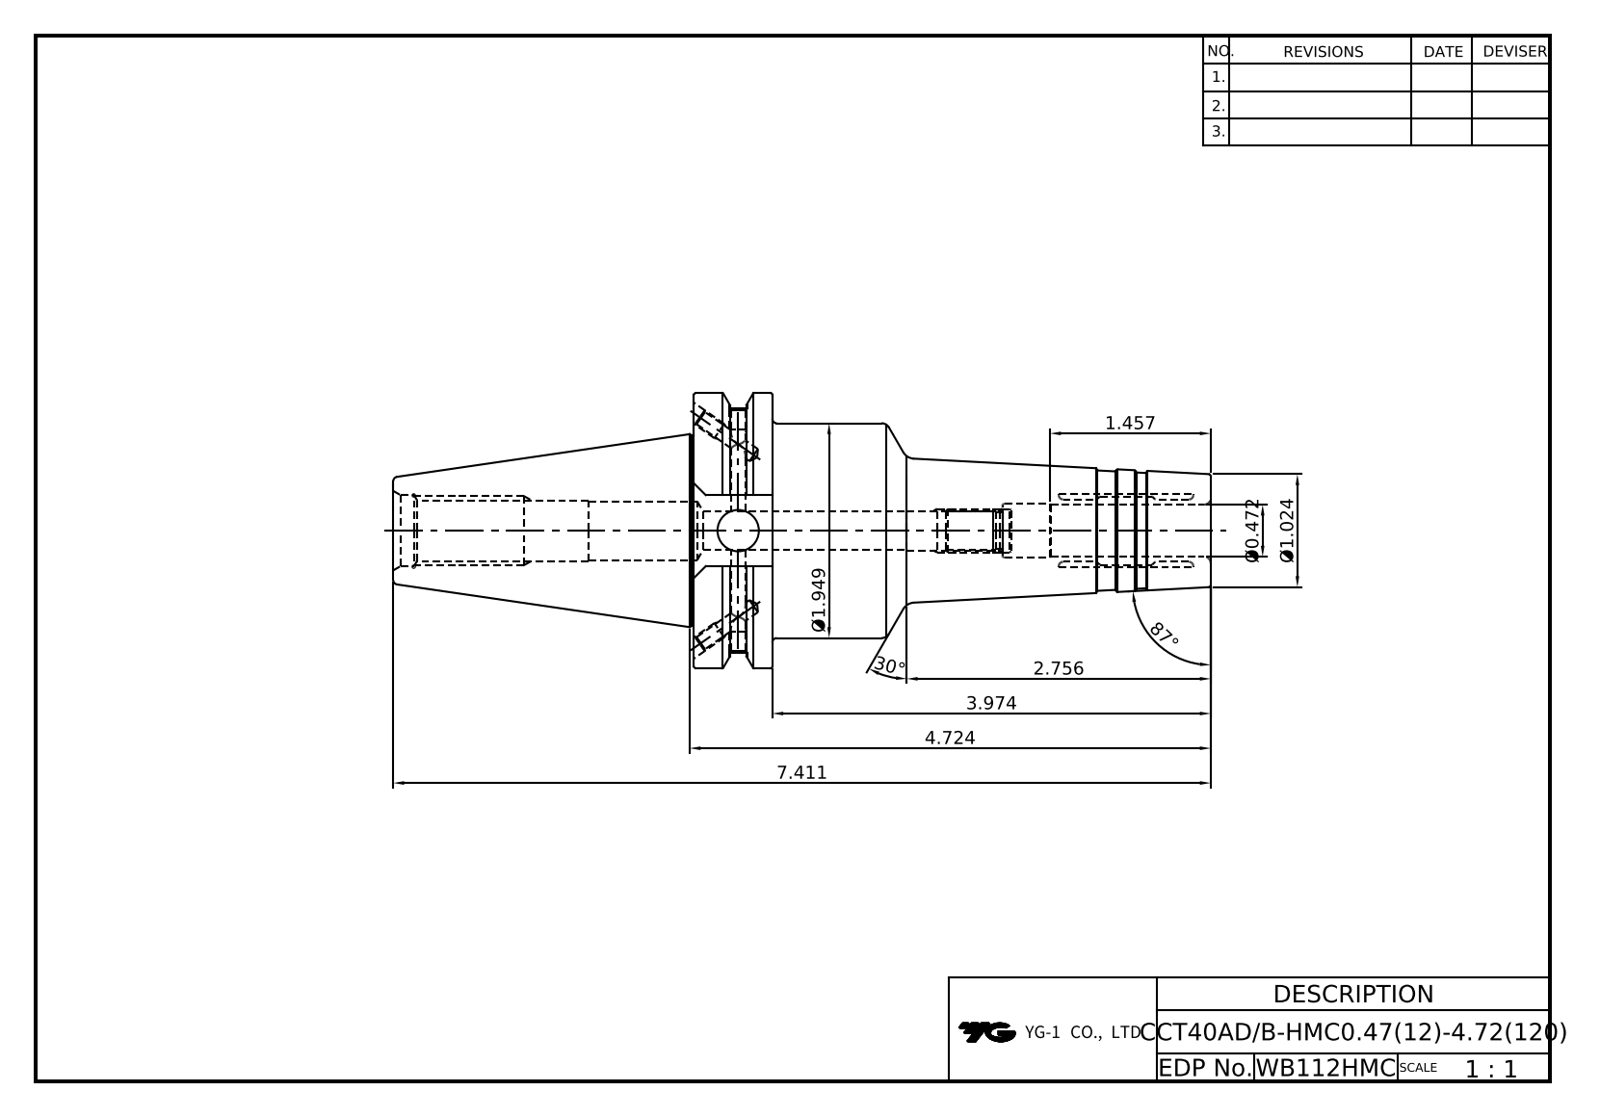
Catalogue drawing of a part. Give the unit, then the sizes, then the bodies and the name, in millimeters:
Units: millimetres
Overall size (bounding box): 188.25 × 63.5 × 61.09
Round holes (diameter × count): ⌀3.24 ×4, ⌀4 ×2, ⌀4.2 ×2, ⌀8.92 ×1, ⌀9.53 ×1, ⌀12 ×1, ⌀12.6 ×1, ⌀13 ×1, ⌀13.39 ×1, ⌀16.3 ×1
Round bosses / shafts (diameter × count): ⌀63.5 ×1, ⌀49.5 ×1, ⌀43.8 ×1
Partial cylindrical surfaces — rounded edges, fillets, slot ends (radius × count): R8.19 ×1, R28.15 ×1
Main face-to-face distances: 18.05, 119, 100.95, 47.6, 16.38, 69.25, 87.3, 188.25, 81.34, 12.09
Volume: 197 704 mm³ · Surface area: 34 360 mm²
Bodies: 1 solid, 106 faces (35 planar, 30 cylindrical, 41 other)
Part name (STEP PRODUCT): LO-CCT40ADB-HMC12-120
STEP written by: Autodesk Inventor 2020 (AUTOMOTIVE_DESIGN)
